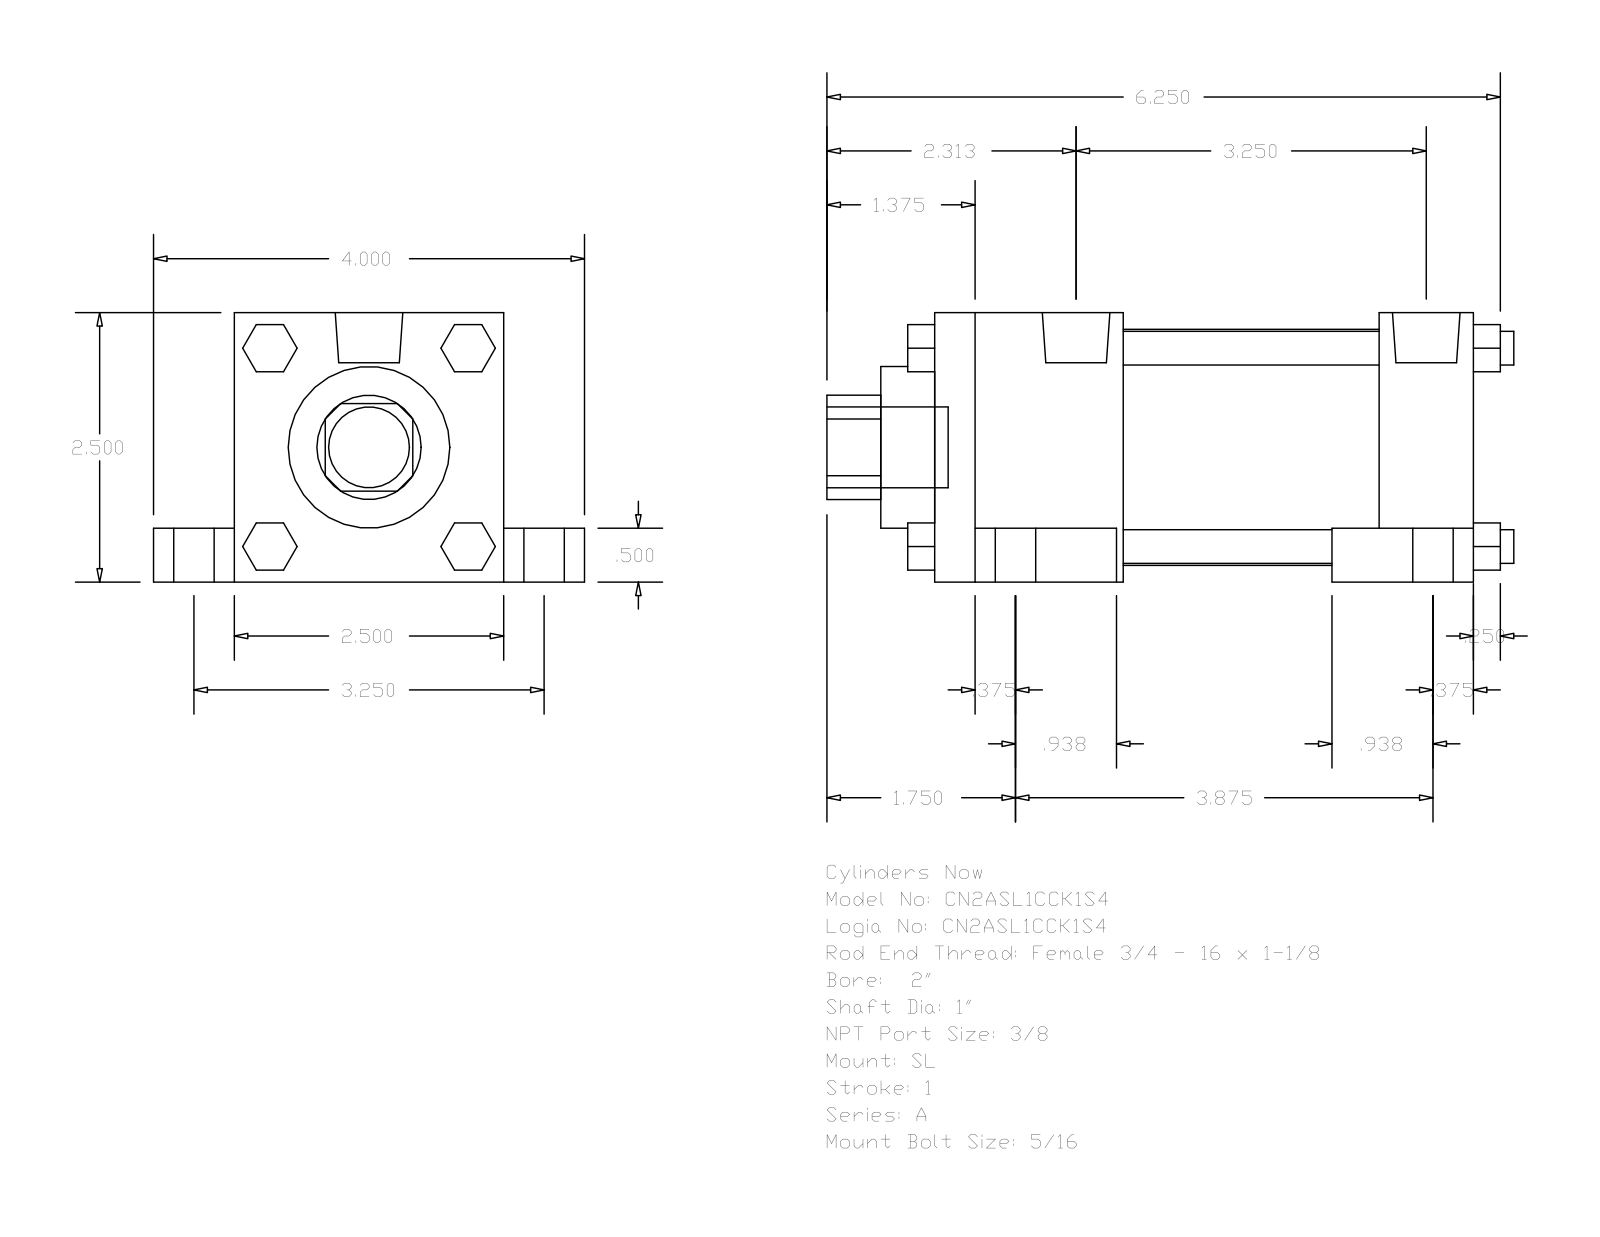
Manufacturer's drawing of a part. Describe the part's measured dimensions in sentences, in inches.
The part is named "A_SL__0200_1". Its 3-D file was written by "GSSL Pune (CONFIG_CONTROL_DESIGN)". It is 0 solids with 148 faces: 112 planar, 36 cylindrical and 0 other. Overall it measures 6.375 by 4 by 2.5 inches. Round holes: 1 of diameter 1, 1 of diameter 1.5, 1 of diameter 2.19. Round bosses or shafts: 4 of diameter 0.625, 4 of diameter 0.375, 4 of diameter 0.313, 4 of diameter 0.219, 2 of diameter 0.627, 1 of diameter 0.75. Partial cylindrical surfaces (rounded edges, fillets, slot ends): 1 of radius 0.484. The main face-to-face distances are 2.5, 3.25, 0.5, 5, 2, 0.875, 0.75, 1.75, 4.125, 2.375.
